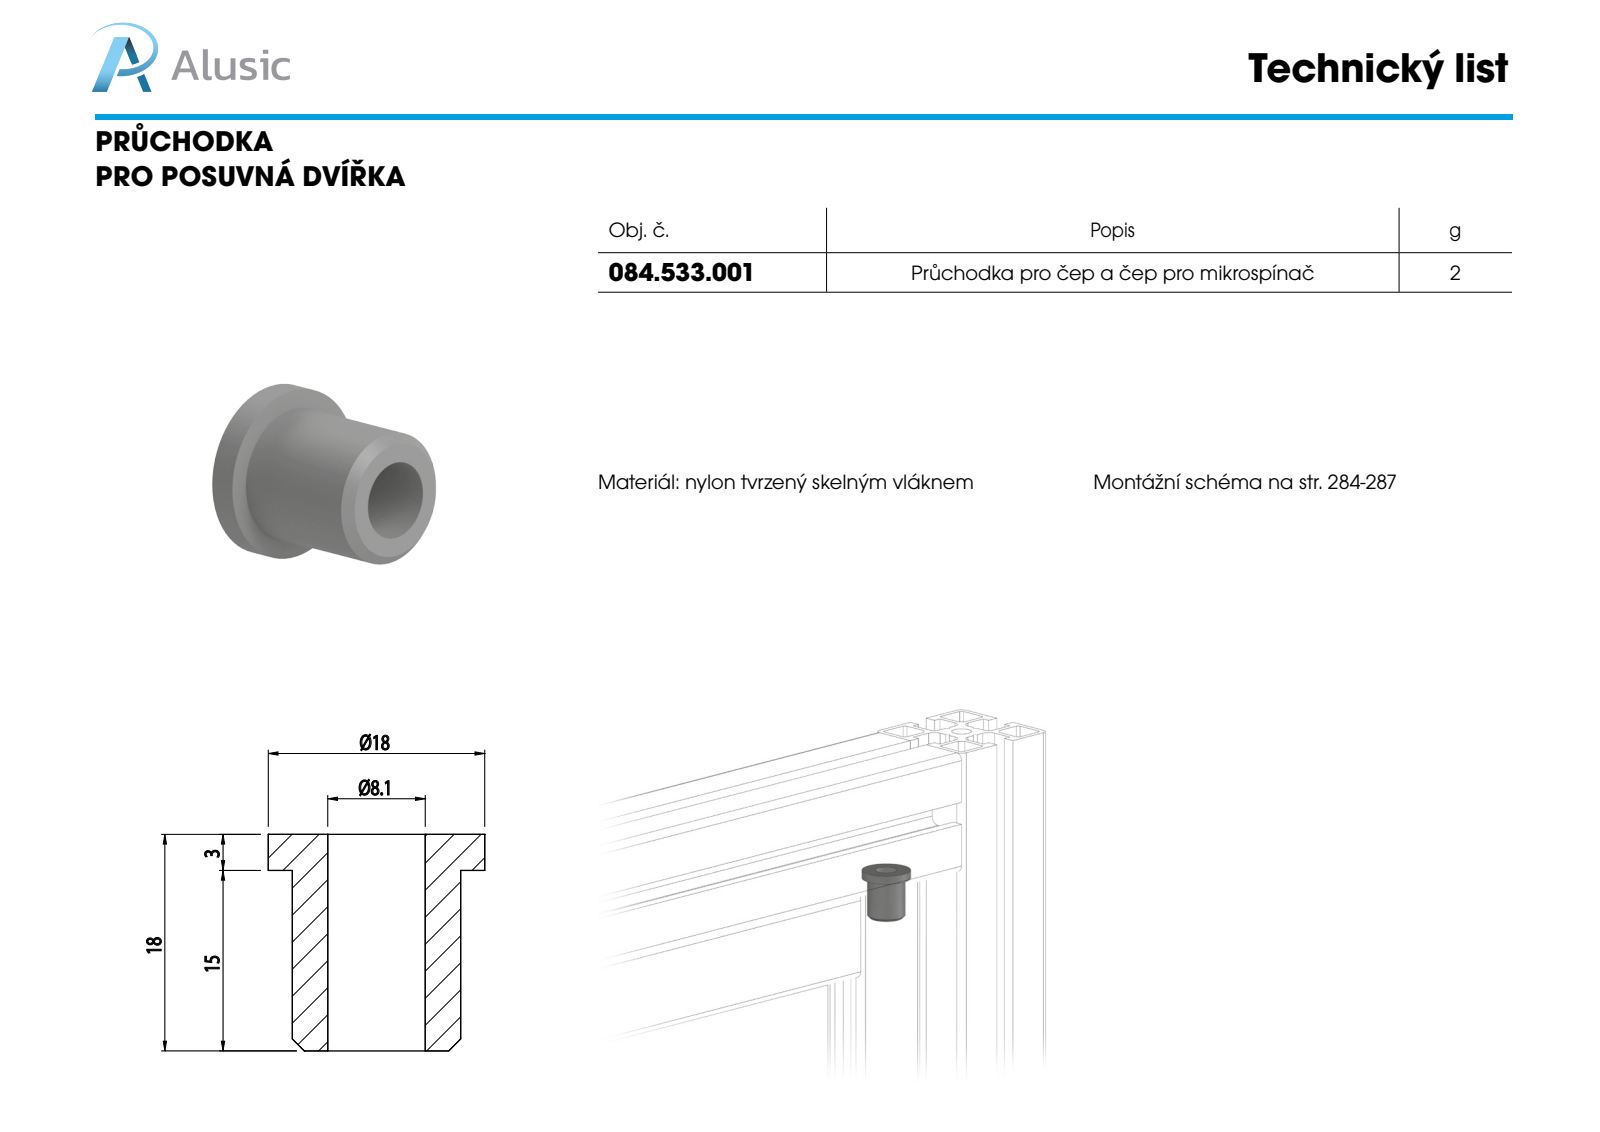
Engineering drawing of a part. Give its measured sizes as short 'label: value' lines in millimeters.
name: 084.533.001
written by: SolidWorks 2011 (CONFIG_CONTROL_DESIGN)
unit: mm
bodies: 1 solid, 11 faces (3 planar, 6 cylindrical, 2 other)
size: 18 × 18 × 18
volume: 2 124 mm³; area: 1 666 mm²
holes: 1× ⌀8.1
bosses: 1× ⌀18, 1× ⌀14
face distances: 3, 18, 15
